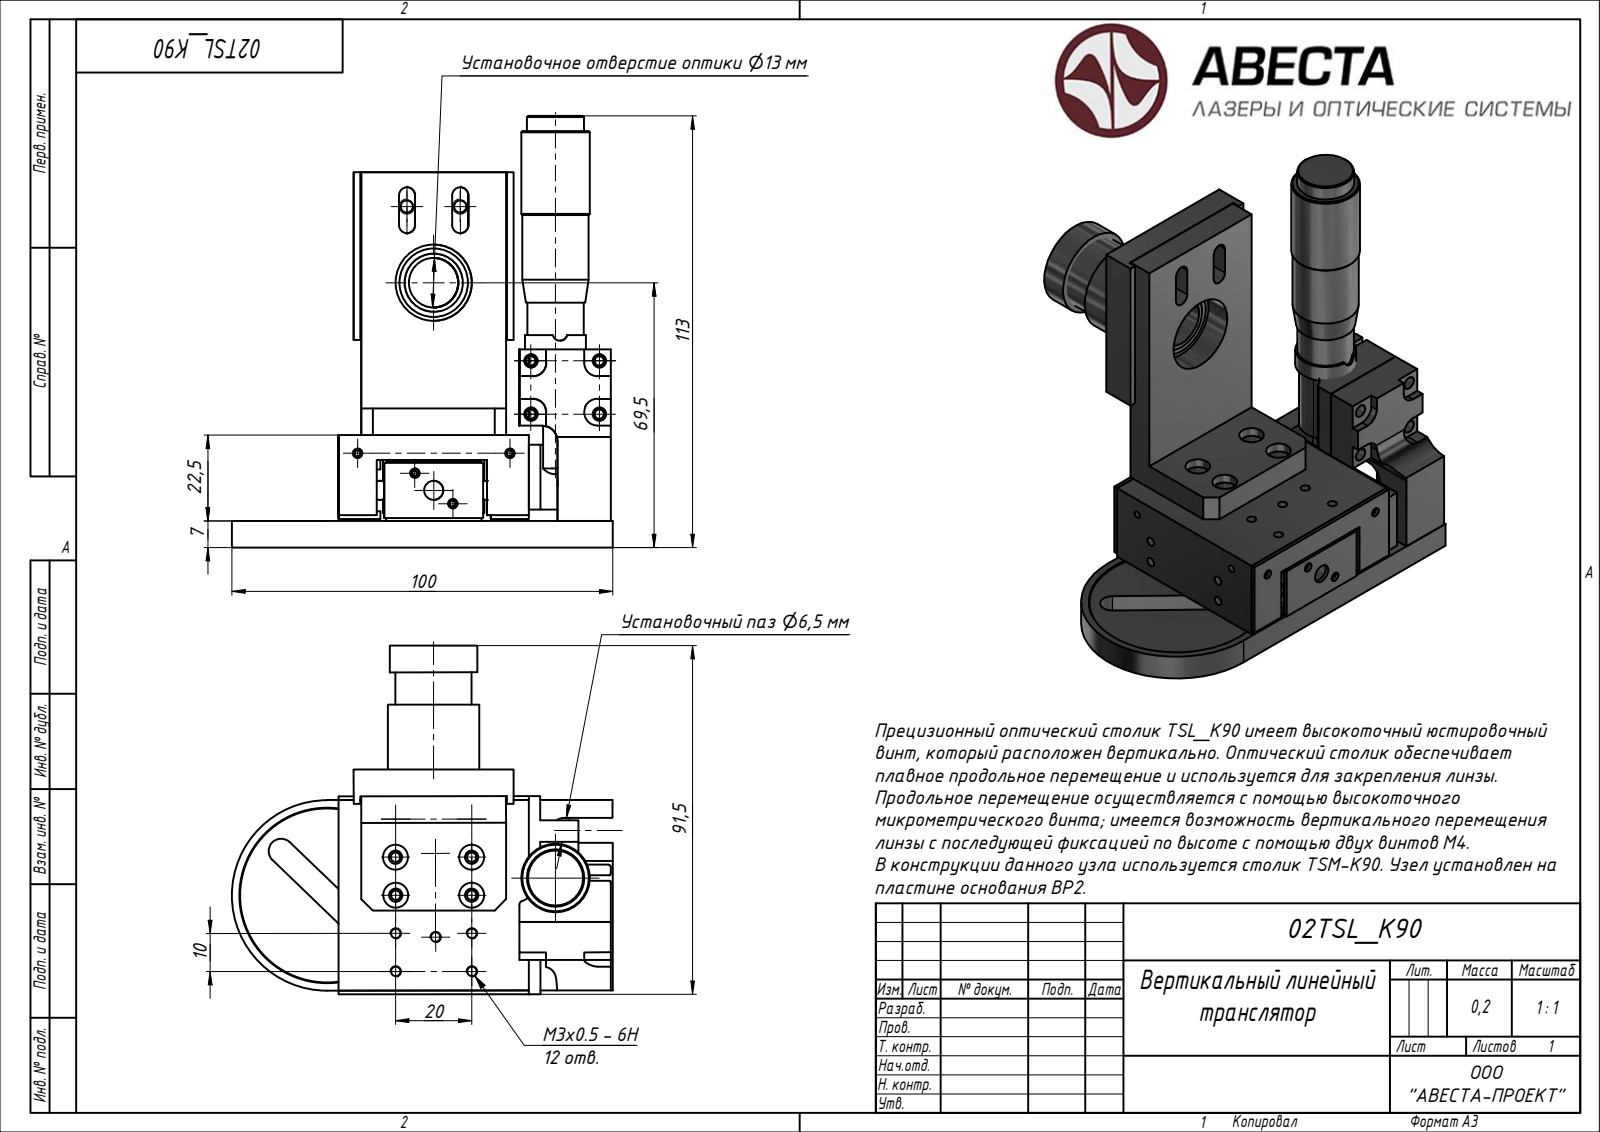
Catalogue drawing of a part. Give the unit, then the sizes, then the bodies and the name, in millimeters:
Units: millimetres
Overall size (bounding box): 113.27 × 100.02 × 95.64
Bodies: 22 solids, 988 faces (0 planar, 0 cylindrical, 988 other)
Part name (STEP PRODUCT): Block 02; Block 01
STEP written by: ST-DEVELOPER v15 (AUTOMOTIVE_DESIGN)
